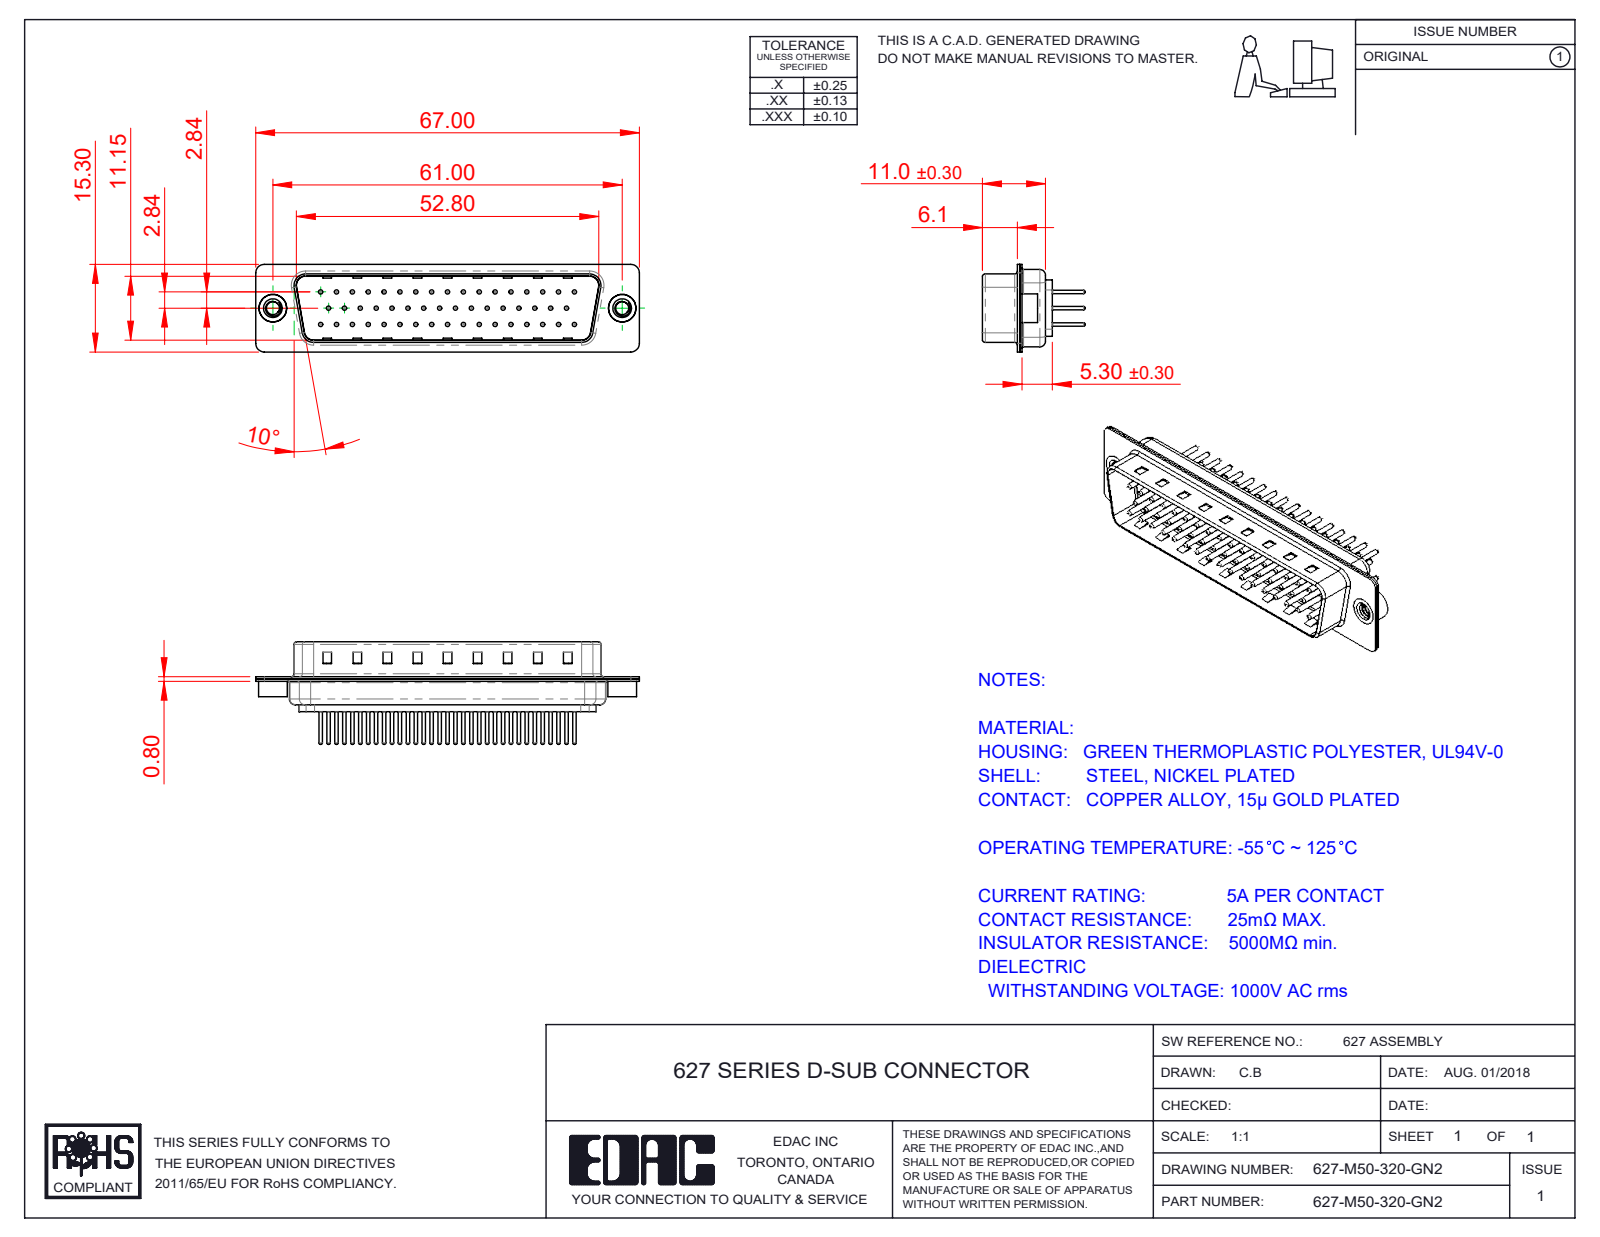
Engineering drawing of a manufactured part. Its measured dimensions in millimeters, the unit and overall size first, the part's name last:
Units: millimetres
Overall size (bounding box): 67 × 17.9 × 15.3
Round holes (diameter × count): ⌀0.75 ×50, ⌀1.6 ×50, ⌀2 ×50, ⌀2.26 ×2, ⌀4 ×2, ⌀4.8 ×2
Round bosses / shafts (diameter × count): ⌀1.5 ×50, ⌀0.6 ×50, ⌀5 ×2, ⌀4.9 ×2
Partial cylindrical surfaces — rounded edges, fillets, slot ends (radius × count): R1.5 ×16, R2 ×12, R0.5 ×8, R1.6 ×8, R0.25 ×4, R0.6 ×4, R0.65 ×4, R0.9 ×4
Main face-to-face distances: 0.4, 11.55, 5.7, 6.1, 0.78, 0.77, 12.33, 12.32, 13.1, 5.3
Hole centre spacings: 3.16, 2.77, 5.54, 8.31, 11.08, 13.85, 16.62, 5.03
Volume: 4 525 mm³ · Surface area: 10 699 mm²
Bodies: 55 solids, 2262 faces (553 planar, 841 cylindrical, 868 other)
Part name (STEP PRODUCT): 627M 4-40 Threaded Rivet; 627M Contact Row 1_20; 627M Shell Rear_50 Contacts; 627M Housing_50 Contacts (+4 more)
STEP written by: SolidWorks 2020 (CONFIG_CONTROL_DESIGN)
